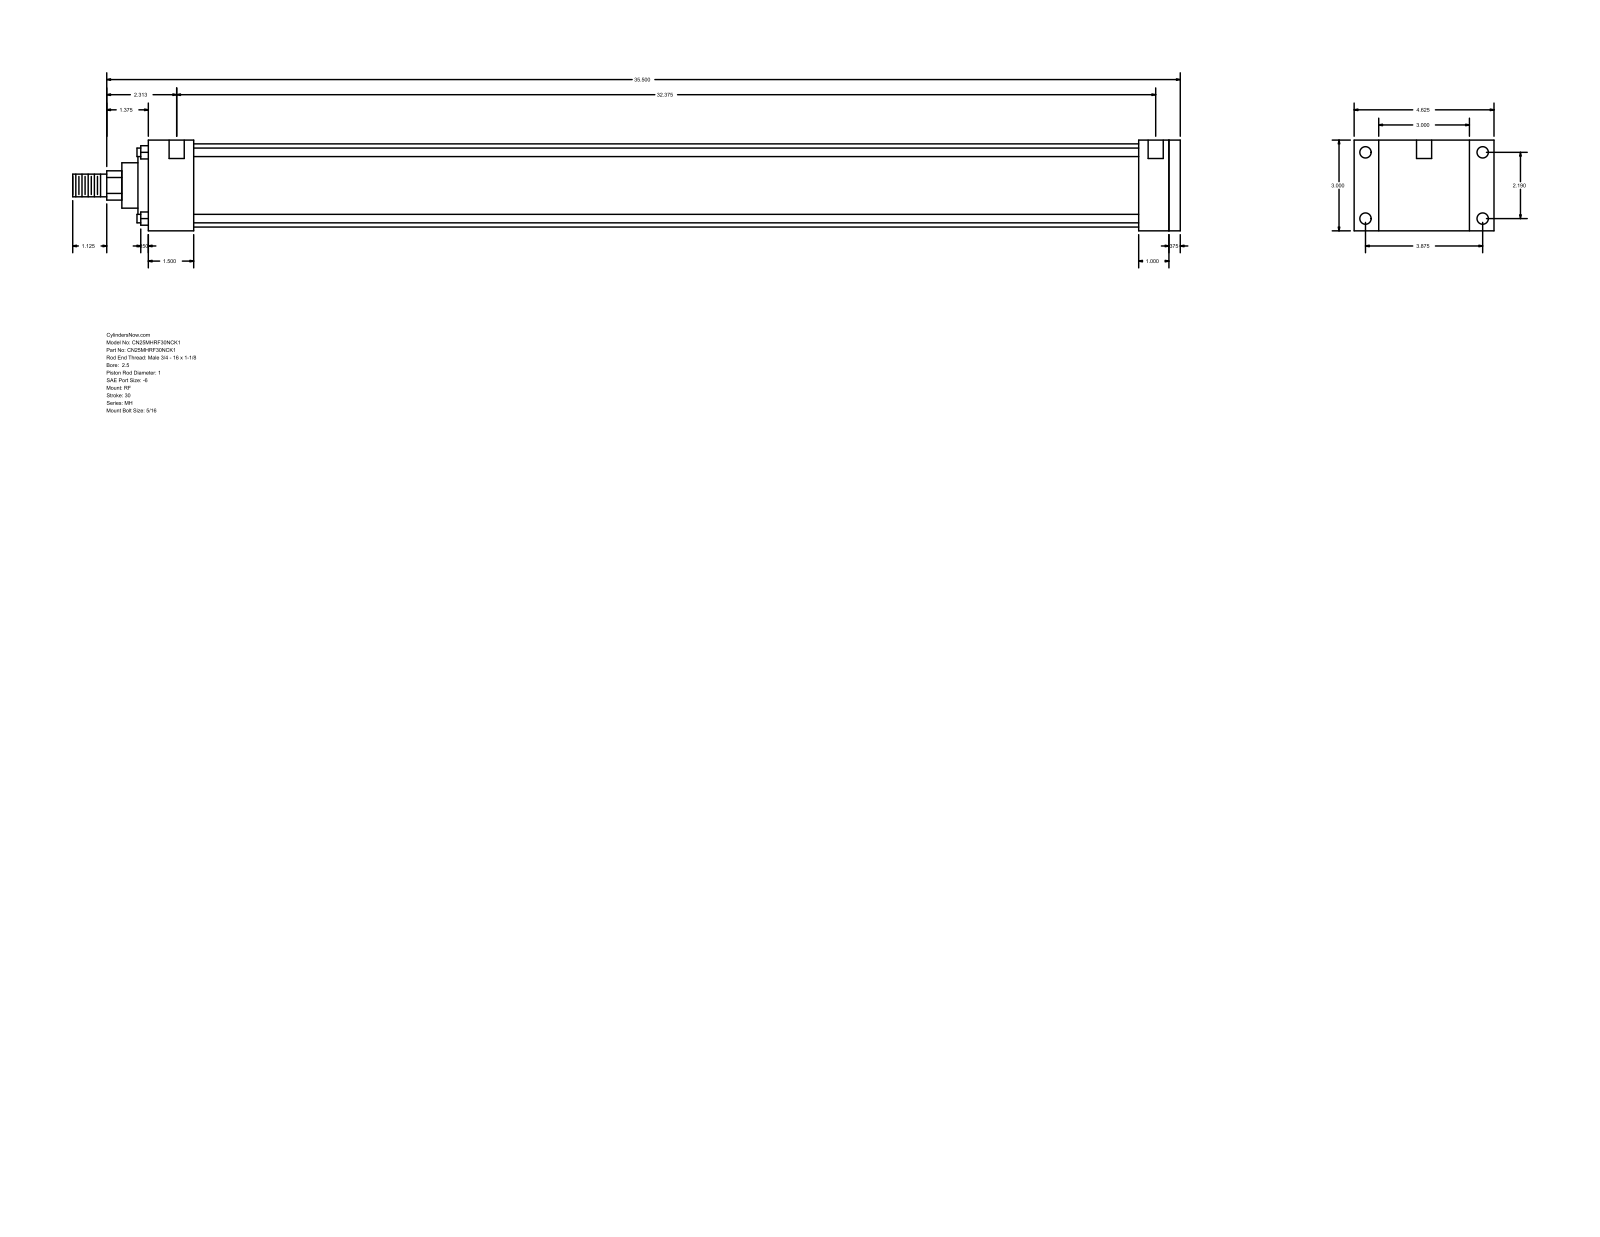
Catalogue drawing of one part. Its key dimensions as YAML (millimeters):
part_name: "MH_RF__0250_1"
step_written_by: "GSSL Pune (CONFIG_CONTROL_DESIGN)"
units: millimeters
bodies: {solids: 0, faces: 94, planar: 65, cylindrical: 29, other: 0}
overall_size: [930.27, 117.47, 76.2]
round_holes:
  - {diameter: 5.56, count: 4}
  - {diameter: 9.53, count: 4}
  - {diameter: 12.7, count: 2}
round_bosses_or_shafts:
  - {diameter: 7.14, count: 4}
  - {diameter: 69.85, count: 1}
  - {diameter: 60.33, count: 1}
  - {diameter: 38.1, count: 1}
  - {diameter: 25.4, count: 1}
  - {diameter: 19.05, count: 1}
partial_cylinders:
  - {radius: 12.29, count: 1}
face_to_face_distances: [76.2, 9.53, 857.25, 866.78, 25.4, 831.85, 34.93, 38.11, 793.74, 819.14]
hole_center_spacings: [55.62, 98.42, 113.05, 830.26, 3.18, 4.76, 822.32, 825.5]
